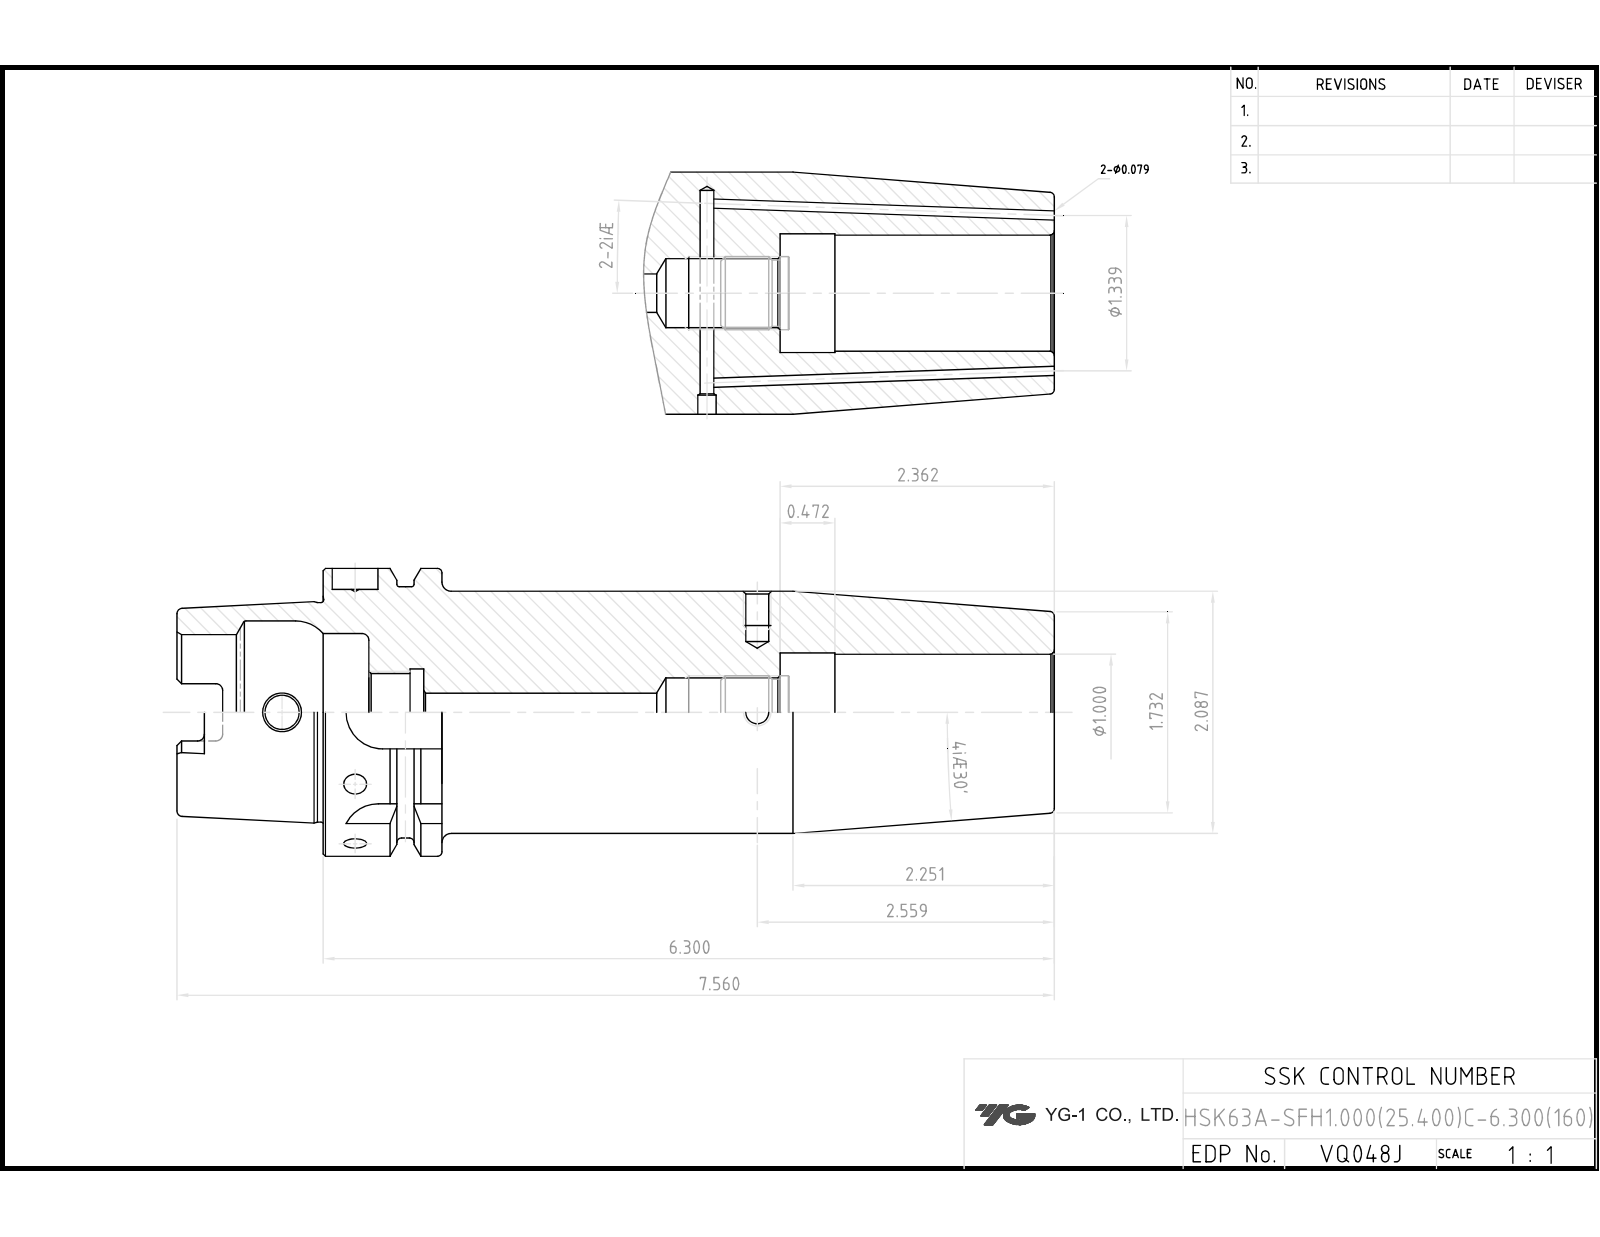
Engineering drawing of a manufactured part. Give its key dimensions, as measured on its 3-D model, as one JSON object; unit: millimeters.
{"part_name": "HSK63A_BALANCE_20200217", "step_written_by": "CREO PARAMETRIC BY PTC INC, 2018500 (CONFIG_CONTROL_DESIGN)", "units": "millimeters", "bodies": {"solids": 1, "faces": 189, "planar": 62, "cylindrical": 57, "other": 70}, "overall_size": [192, 63, 63], "volume_mm3": 318463, "surface_area_mm2": 52249, "round_holes": [[5, 2], [7.5, 1], [8.4, 1], [10, 1], [15, 1], [16, 1], [17, 1], [18, 1], [19, 1], [25.4, 1], [26, 1], [34, 1]], "round_bosses_or_shafts": [[63, 1], [55, 1], [53, 1], [48.04, 1]], "partial_cylinders_radius": [[1.5, 6], [2.88, 4], [8, 4]], "face_to_face_distances": [160, 10, 150, 26, 32, 16, 134, 58, 6.12, 9.88]}
